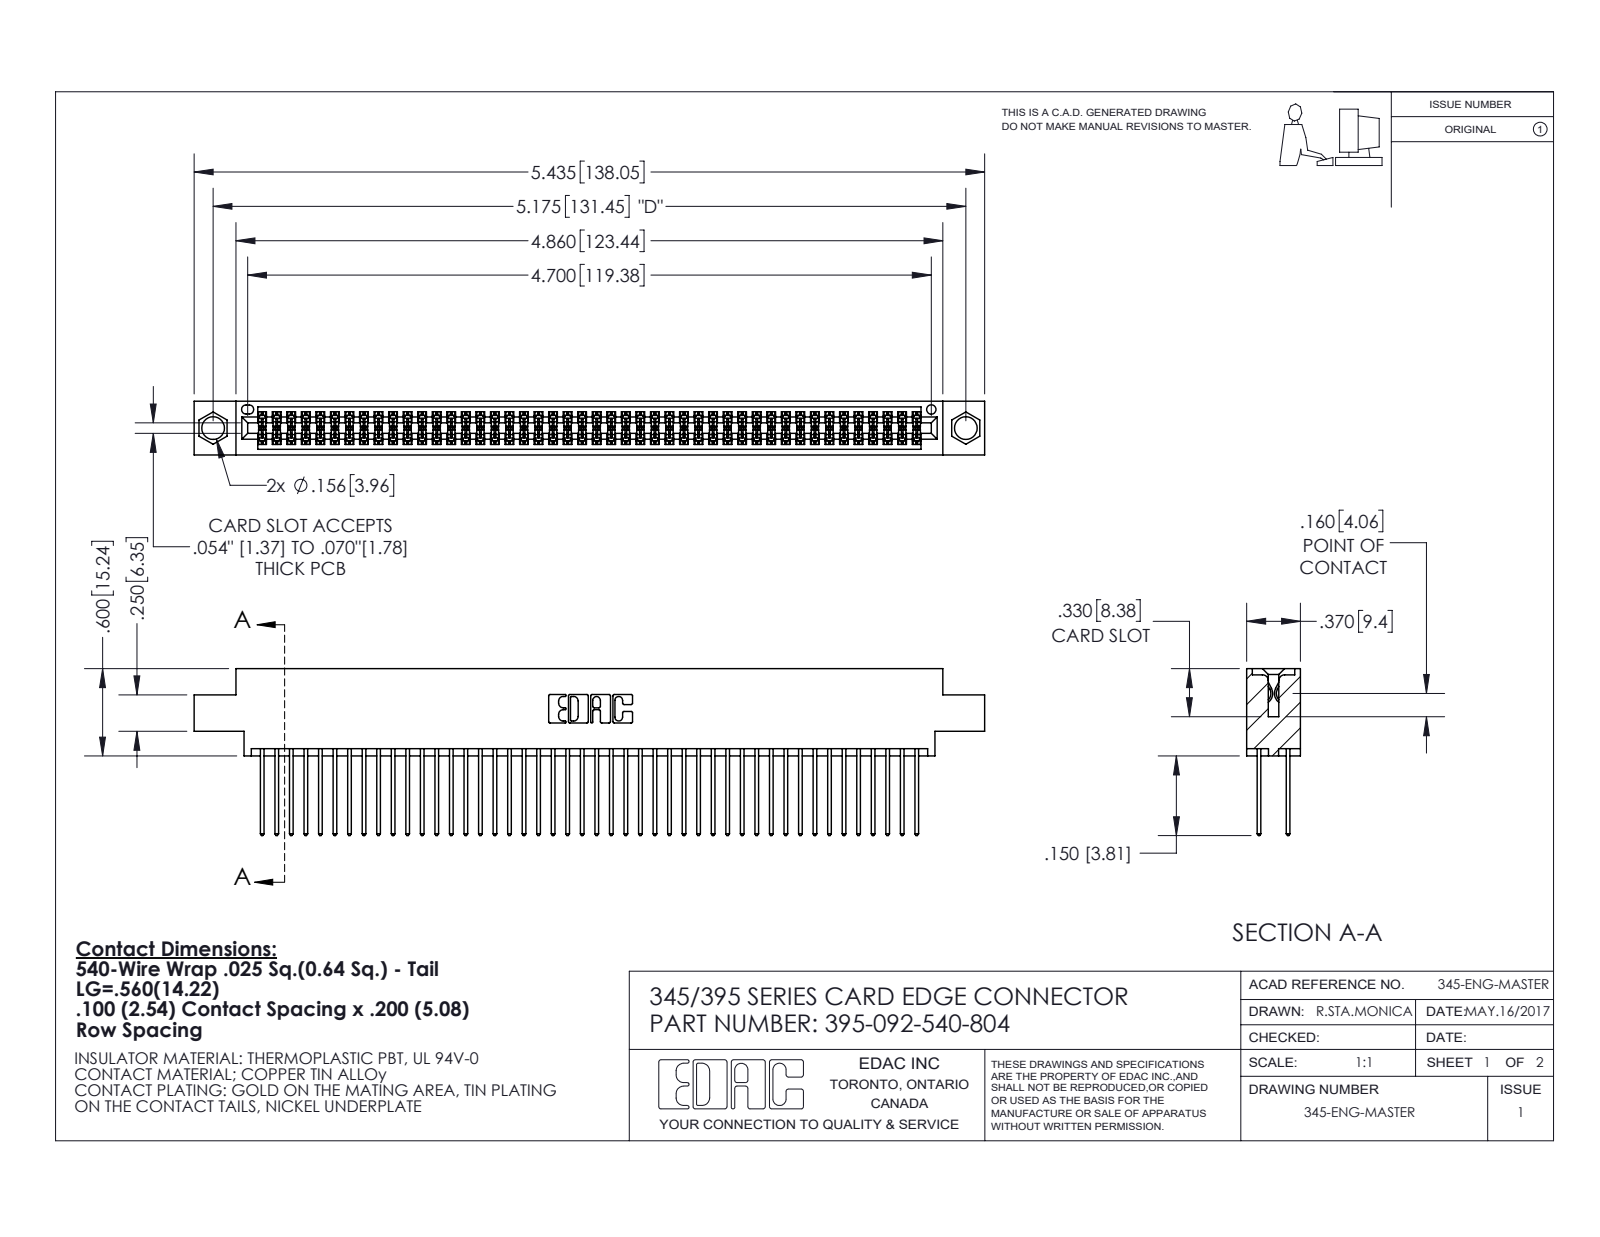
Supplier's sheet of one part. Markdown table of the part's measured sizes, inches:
| quantity | value |
| --- | --- |
| part name | 395-092-540-804; 345-292-001_345-293-140; 345 Part_0.170 Offset - 0.156 Dia-TI |
| STEP written by | SolidWorks 2020 (CONFIG_CONTROL_DESIGN) |
| units | inches |
| bodies | 93 solids, 4744 faces (3134 planar, 1610 cylindrical, 0 other) |
| overall size | 5.435 × 1.147 × 0.37 |
| volume | 0.829 in³ |
| surface area | 33.73 in² |
| round holes (diameter × count) | 0.156 × 2, 0.064 × 1 |
| partial cylindrical surfaces (radius × count) | 0.006 × 184, 0.01 × 92, 0.01 × 22, 0.007 × 6, 0.031 × 6, 0.026 × 3, 0.014 × 2, 0.019 × 2 |
| main face-to-face distances | 0.072, 0.298, 0.2, 0.098, 0.272, 0.025, 0.37, 0.225, 0.175, 0.149 |
| hole center spacings | 0.27, 4.939, 5.175 |
